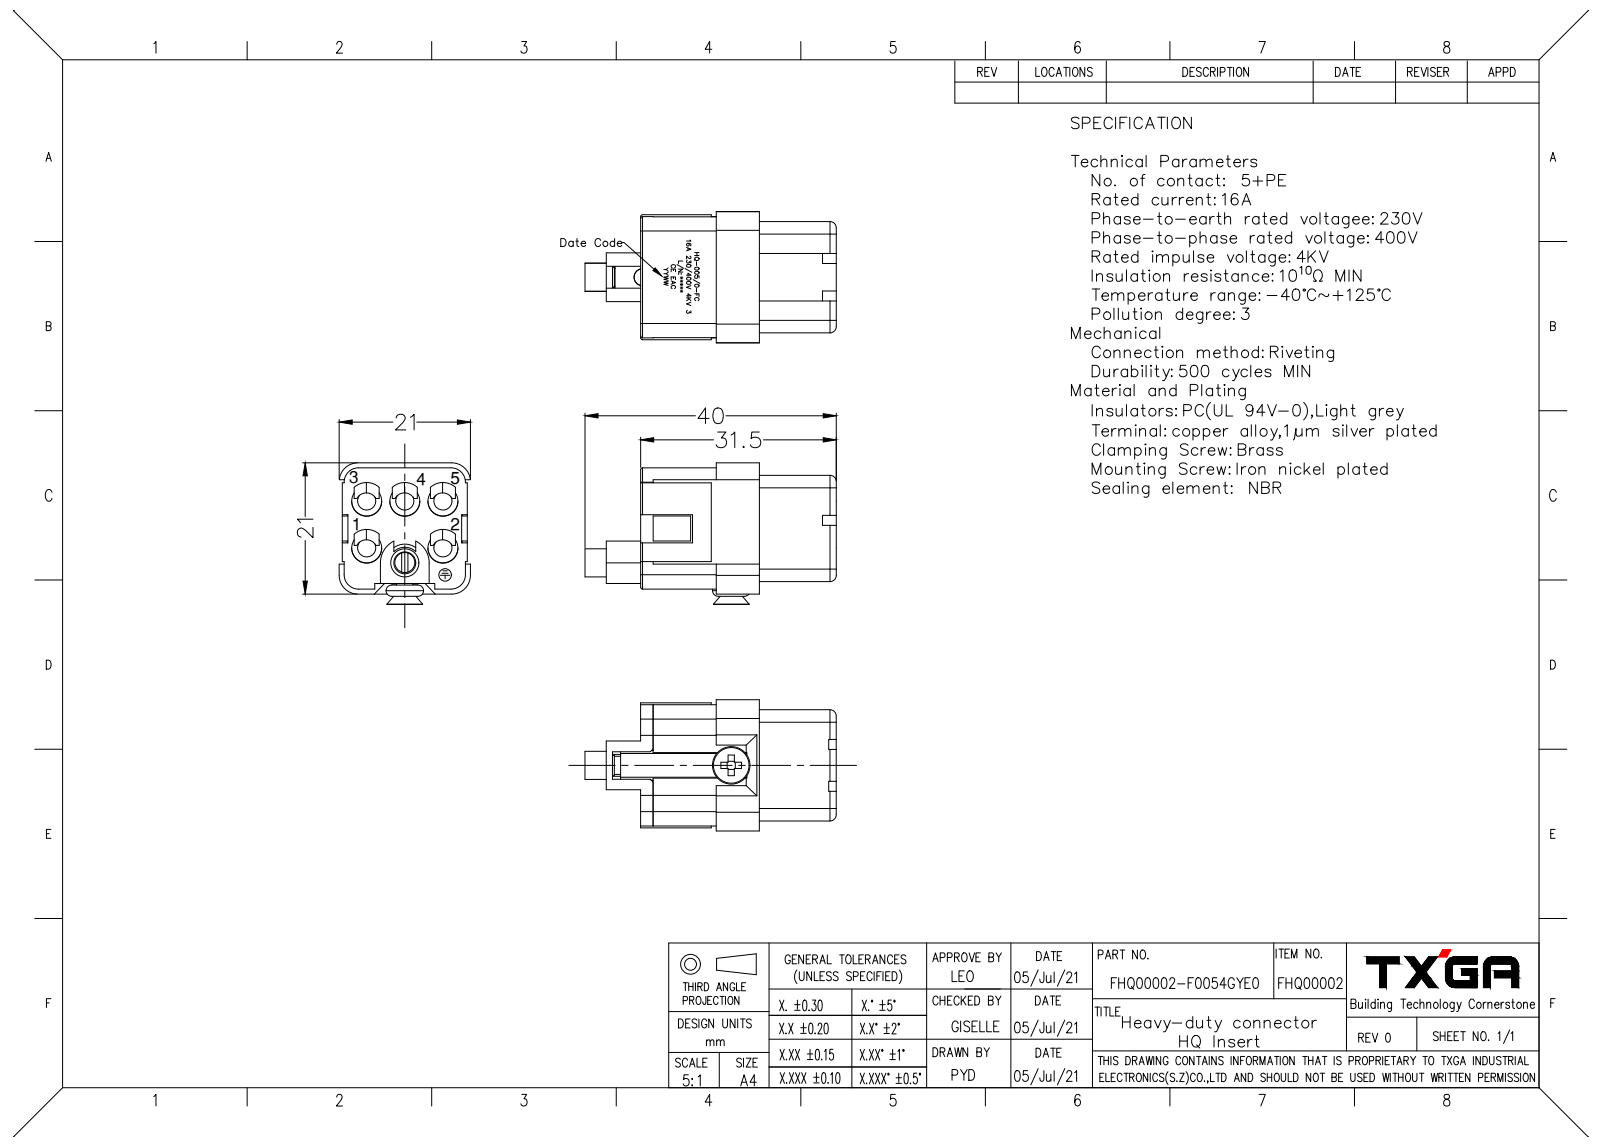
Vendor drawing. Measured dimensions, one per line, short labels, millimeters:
name: FHQ00002-F0054GYE0 HQ-005&0-FC
written by: SolidWorks 2021 (CONFIG_CONTROL_DESIGN)
unit: mm
bodies: 1 solid, 451 faces (277 planar, 89 cylindrical, 85 other)
size: 40.2 × 22.65 × 21
volume: 7 483 mm³; area: 8 530 mm²
holes: 5× ⌀4.8, 1× ⌀2.7, 1× ⌀3.34, 1× ⌀3.5, 1× ⌀4.7
bosses: 1× ⌀5.7, 1× ⌀4.5, 1× ⌀4.35, 1× ⌀3.2, 1× ⌀2.9, 1× ⌀2.6
rounds: 10× R3, 6× R0.3, 6× R2.3, 6× R2.4, 5× R1.73, 5× R4.25, 4× R1, 4× R2
face distances: 0.8, 18.2, 18, 0.9, 1.1, 17, 19, 18.9, 17.8, 19.1
hole spacings: 6.1, 6.54, 6.56, 7.5, 9.67, 11.59, 11.63, 12.2
